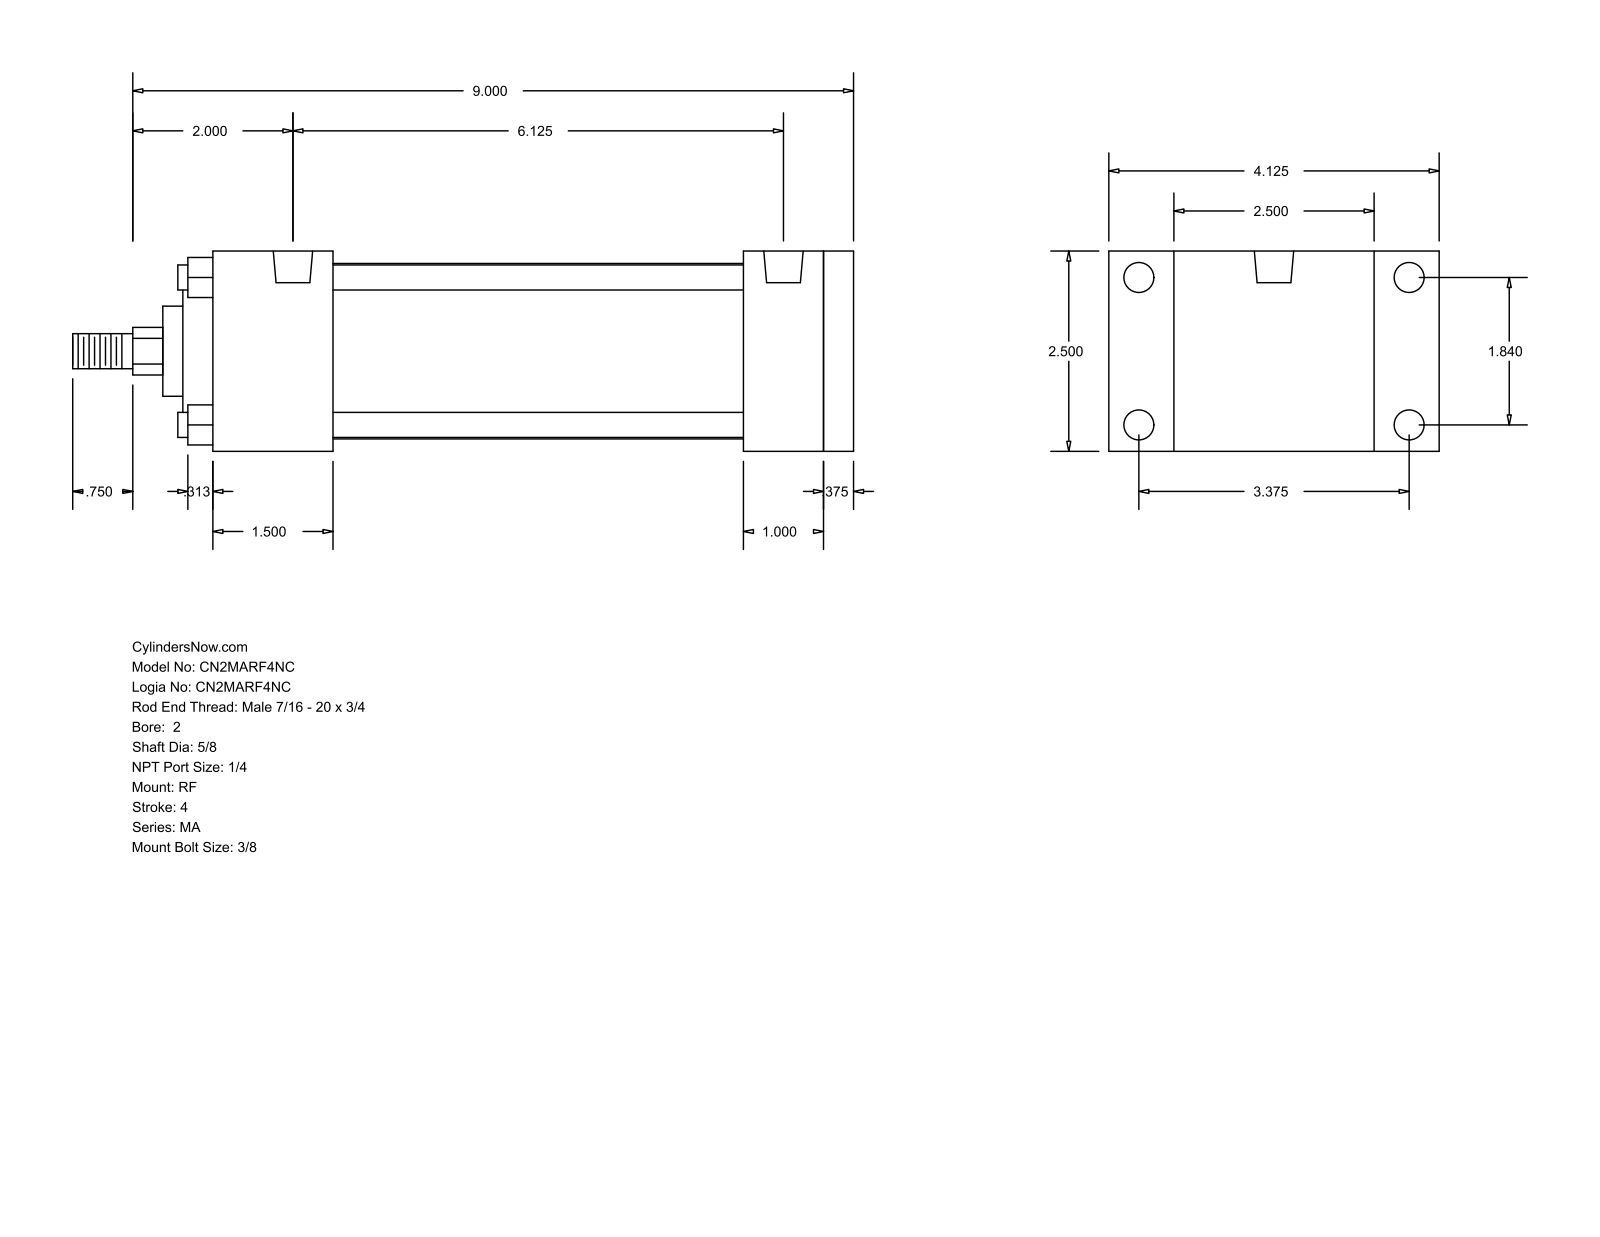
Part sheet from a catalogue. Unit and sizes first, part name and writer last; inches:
Units: inches
Overall size (bounding box): 9.75 × 4.125 × 2.5
Round holes (diameter × count): ⌀0.313 ×4, ⌀0.375 ×4, ⌀0.492 ×2
Round bosses / shafts (diameter × count): ⌀0.313 ×4, ⌀2.19 ×1, ⌀2 ×1, ⌀1.125 ×1, ⌀0.625 ×1, ⌀0.437 ×1
Partial cylindrical surfaces — rounded edges, fillets, slot ends (radius × count): R0.297 ×1
Main face-to-face distances: 2.5, 0.375, 1.5, 7.625, 8, 8.375, 6.125, 6.5, 6.625, 5.125
Hole centre spacings: 1.84, 3.375, 3.844, 6.125
Bodies: 0 solids, 94 faces (65 planar, 29 cylindrical, 0 other)
Part name (STEP PRODUCT): MA_RF__0200_0.625
STEP written by: GSSL Pune (CONFIG_CONTROL_DESIGN)
